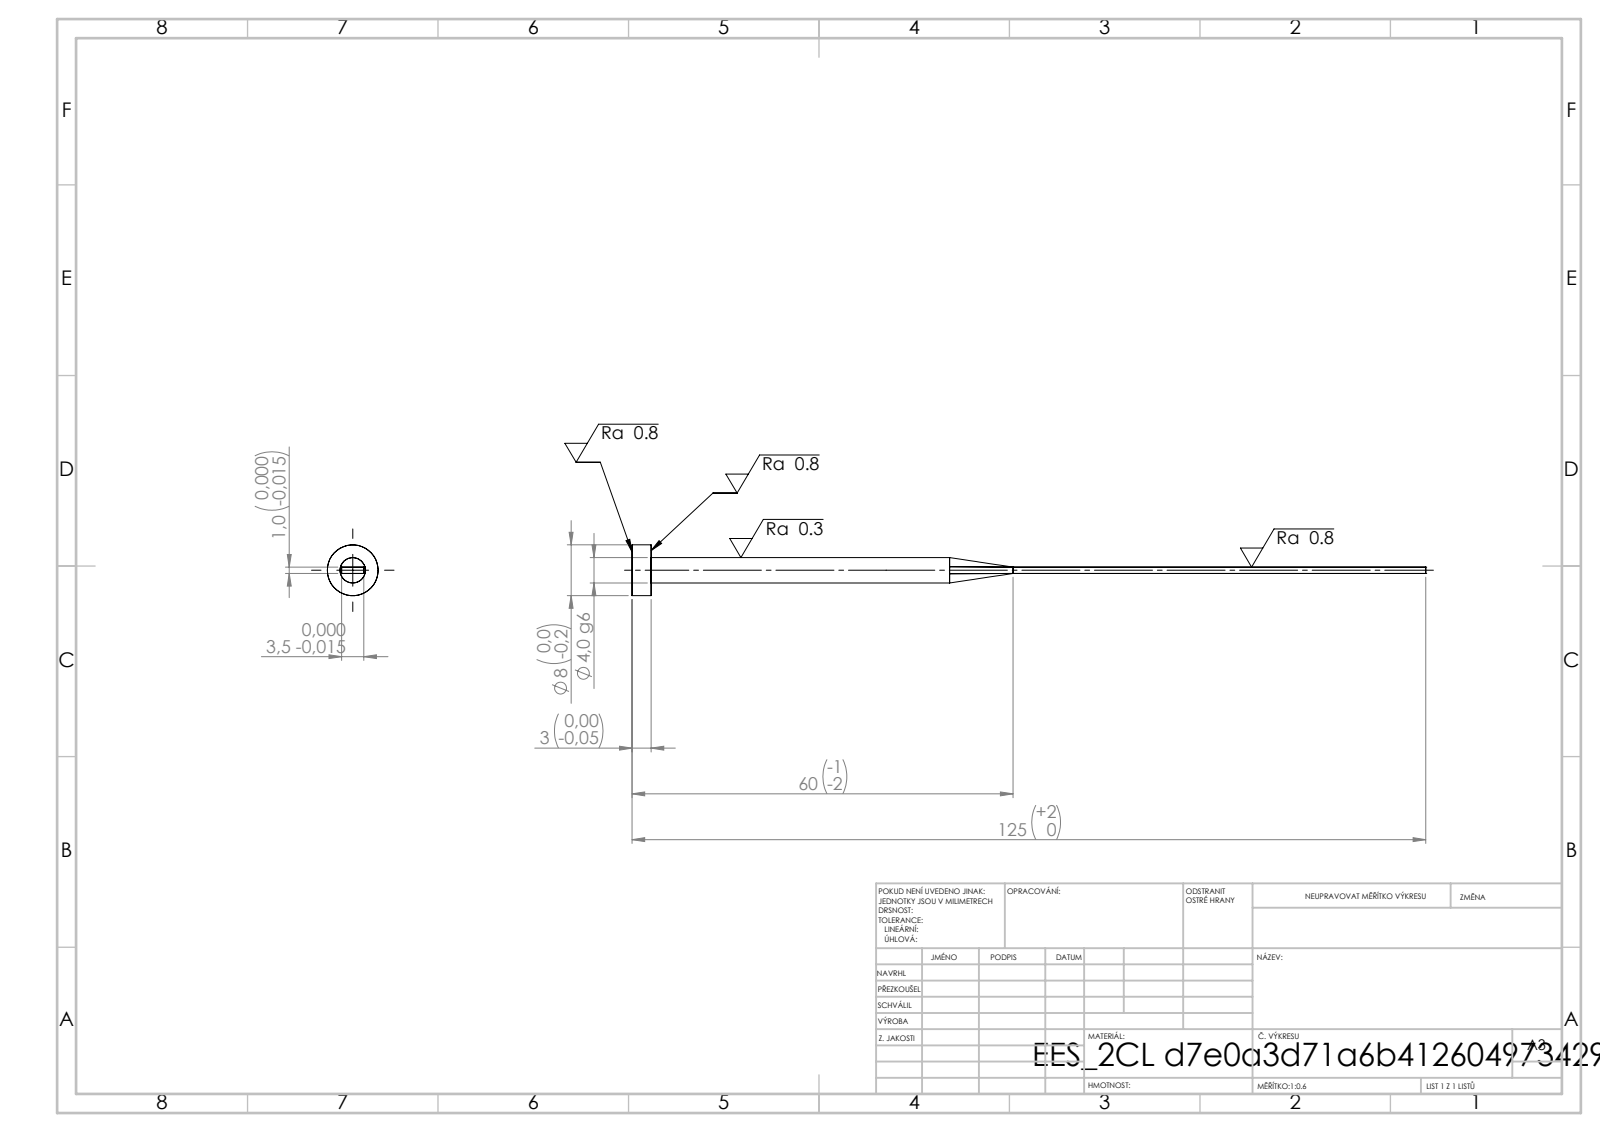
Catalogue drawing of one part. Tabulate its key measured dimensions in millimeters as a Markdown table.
| quantity | value |
| --- | --- |
| STEP written by | SolidWorks 2019 (CONFIG_CONTROL_DESIGN) |
| units | millimeters |
| bodies | 1 solid, 15 faces (7 planar, 4 cylindrical, 4 other) |
| overall size | 125 × 8 × 8 |
| volume | 1 046 mm³ |
| surface area | 1 447 mm² |
| round bosses / shafts (diameter × count) | 8 × 1, 4 × 1 |
| main face-to-face distances | 1, 3.5, 3, 125, 122 |
